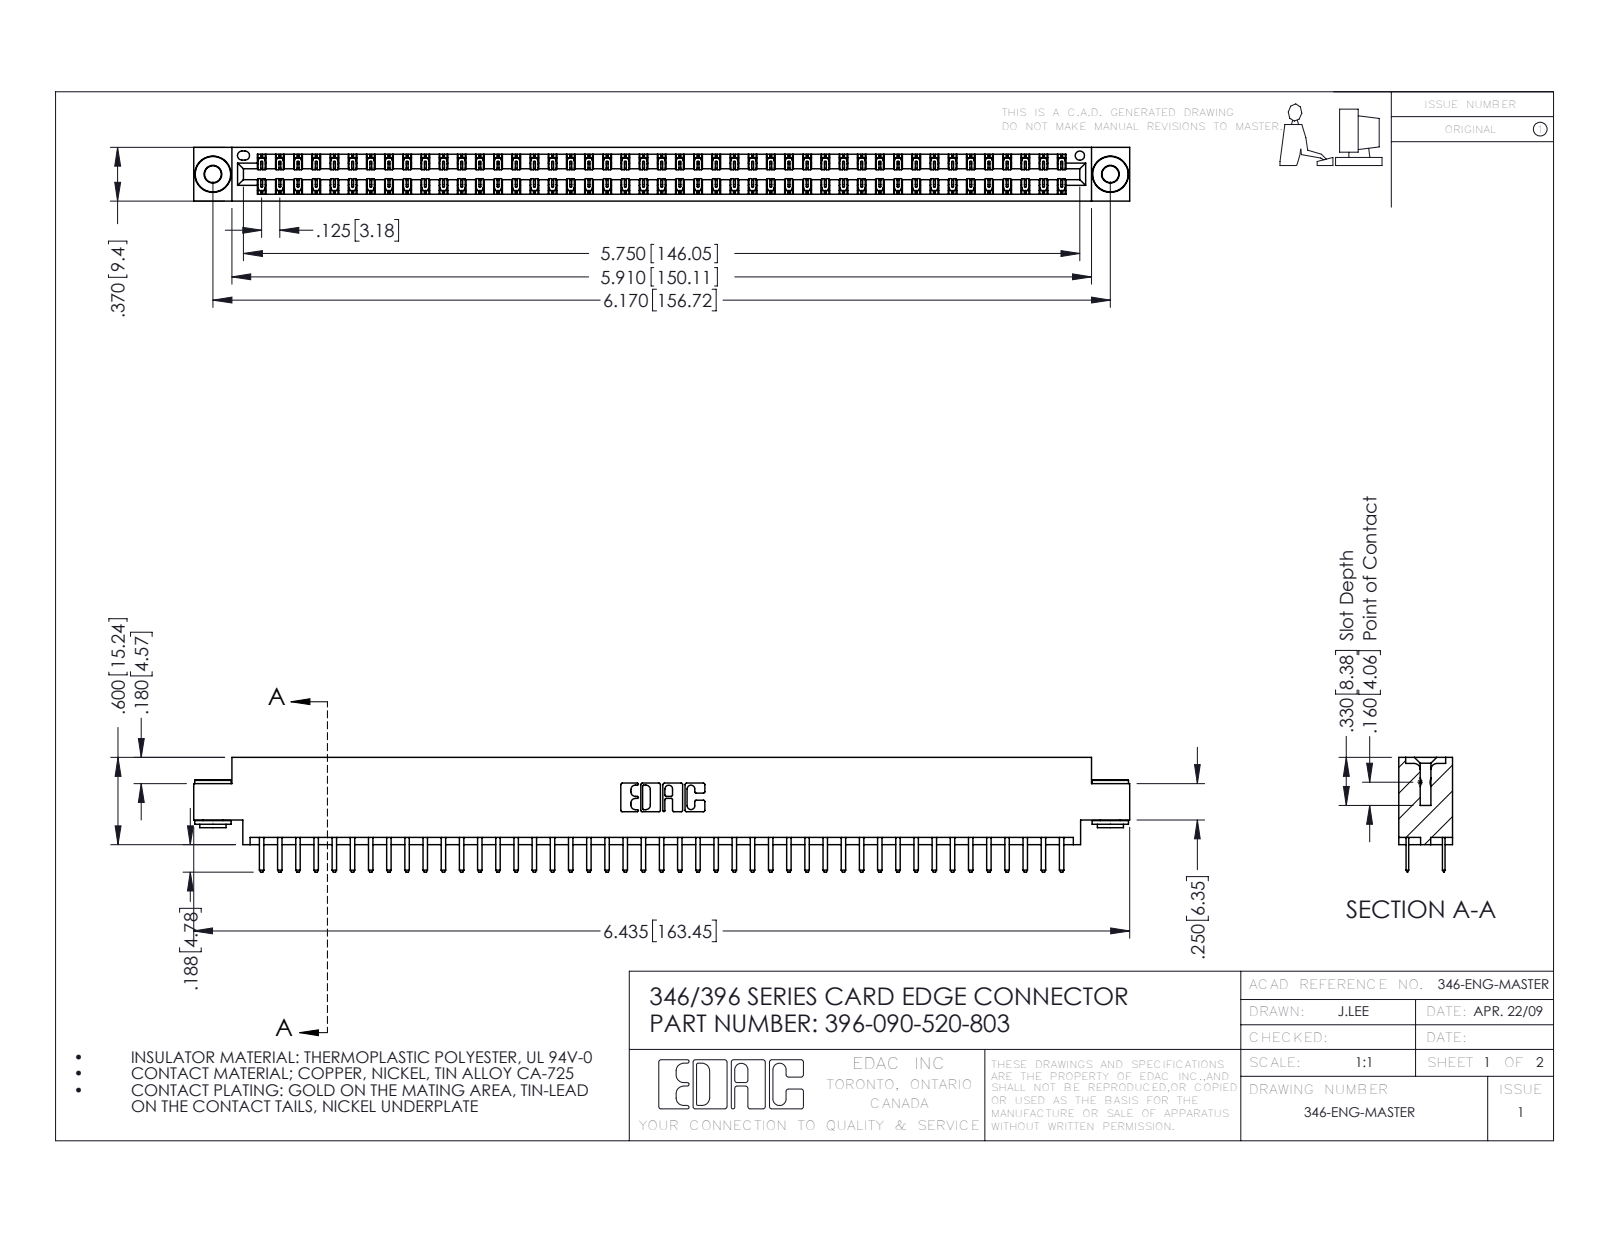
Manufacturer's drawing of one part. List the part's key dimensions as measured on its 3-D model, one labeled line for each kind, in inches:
Part name (STEP PRODUCT): 346 Part_0.170 Offset - 0.156 Dia-TH; 396-090-520-803; 345-292-001_345-293-120; 345-250-002_345-250-002-102
STEP written by: SolidWorks 2016 (CONFIG_CONTROL_DESIGN)
Units: inches
Bodies: 93 solids, 5204 faces (3420 planar, 1776 cylindrical, 8 other)
Overall size (bounding box): 6.435 × 0.788 × 0.37
Volume: 0.963 in³ · Surface area: 34.17 in²
Round holes (diameter × count): ⌀0.116 ×2, ⌀0.156 ×2, ⌀0.064 ×1
Round bosses / shafts (diameter × count): ⌀0.25 ×2, ⌀0.18 ×2, ⌀0.136 ×2
Partial cylindrical surfaces — rounded edges, fillets, slot ends (radius × count): R0.006 ×135, R0.01 ×94, R0.01 ×22, R0.007 ×6, R0.031 ×6, R0.026 ×3, R0.014 ×2, R0.022 ×2
Main face-to-face distances: 0.048, 0.322, 0.25, 0.37, 0.025, 0.275, 0.072, 0.298, 0.148, 0.222
Hole centre spacings: 0.246, 5.961, 6.17
